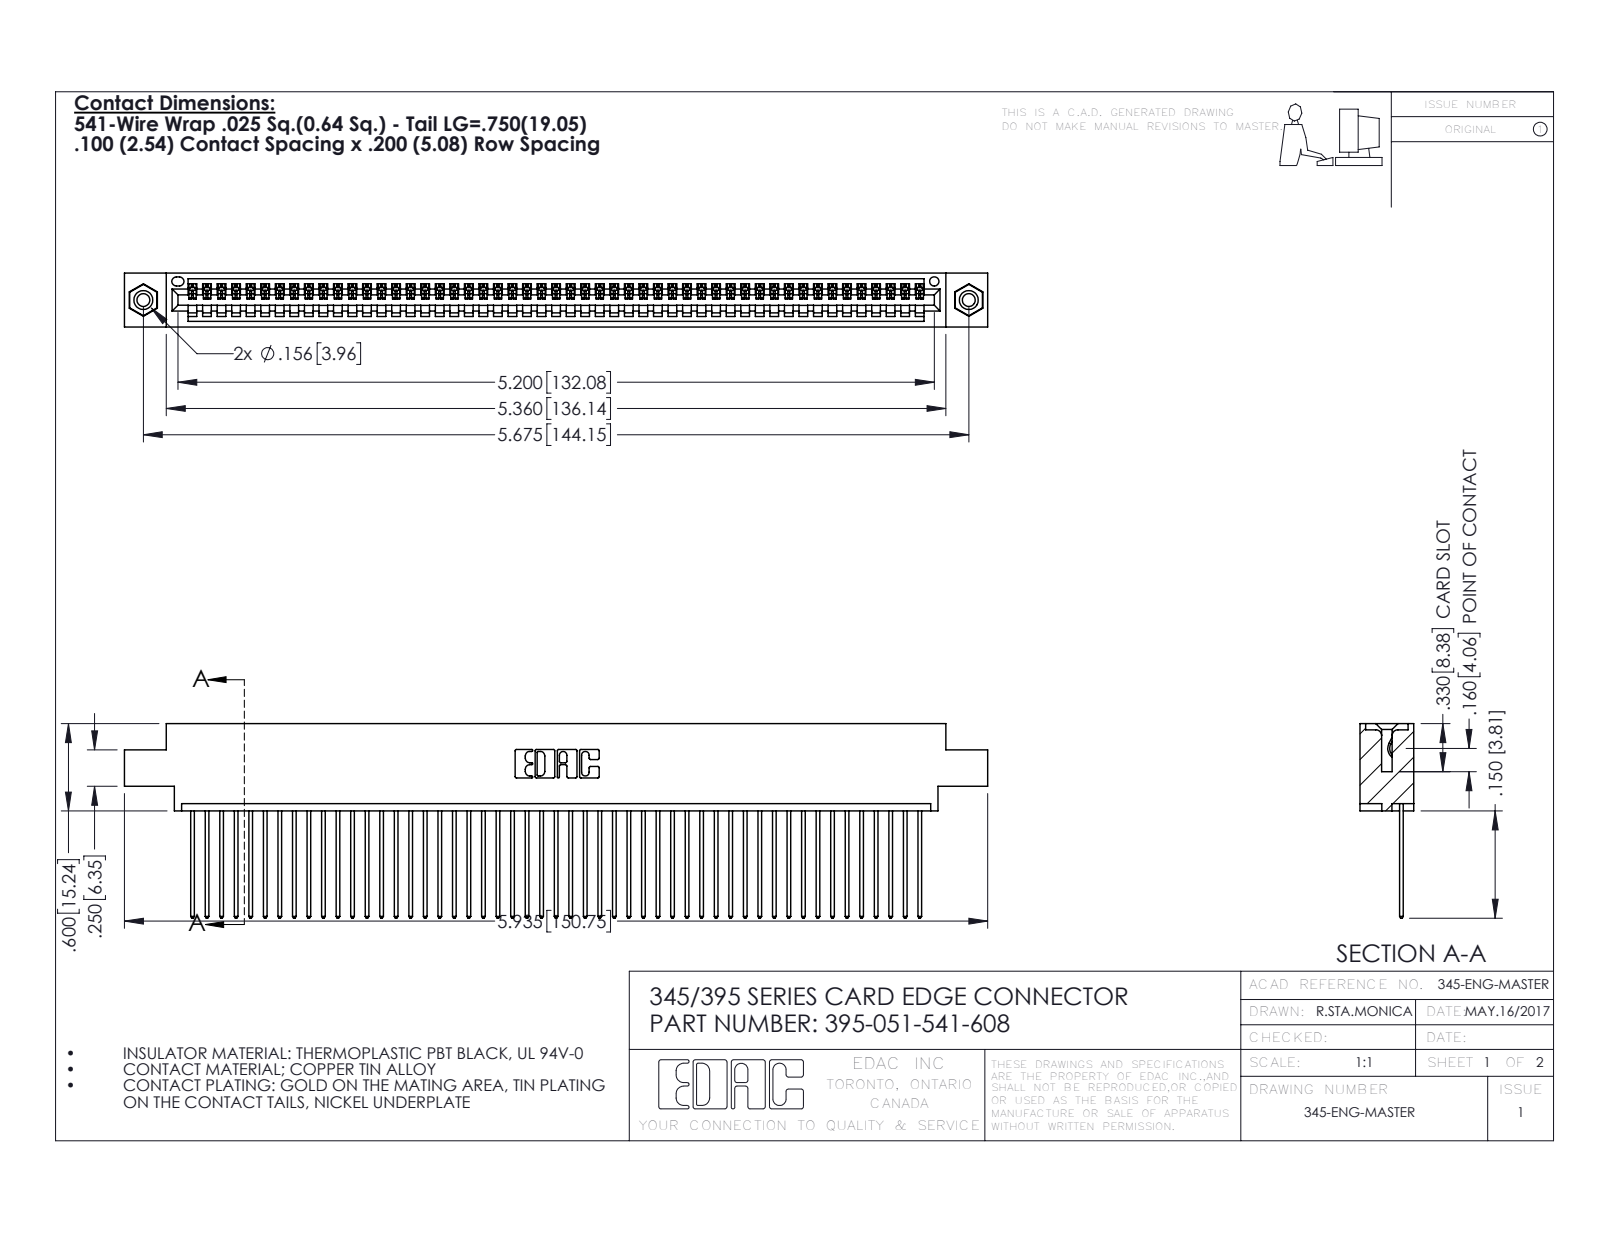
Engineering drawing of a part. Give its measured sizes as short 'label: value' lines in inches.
name: 395-051-541-608; 345-250-001_345-250-003-102; 345-292-001_345-293-141; 345 Part_0.170 Offset - 0.156 Dia-TI
written by: SolidWorks 2016 (CONFIG_CONTROL_DESIGN)
unit: in
bodies: 54 solids, 3148 faces (2156 planar, 976 cylindrical, 16 other)
size: 5.935 × 1.337 × 0.37
volume: 0.881 in³; area: 31.69 in²
holes: 2× ⌀0.089, 2× ⌀0.125, 2× ⌀0.156, 1× ⌀0.064
bosses: 2× ⌀0.155
rounds: 102× R0.006, 102× R0.01, 22× R0.01, 6× R0.007, 6× R0.031, 3× R0.026, 2× R0.031, 2× R0.04
face distances: 0.072, 0.298, 0.098, 0.272, 0.025, 0.37, 0.2, 0.225, 0.175, 0.149
hole spacings: 0.27, 5.439, 5.675
